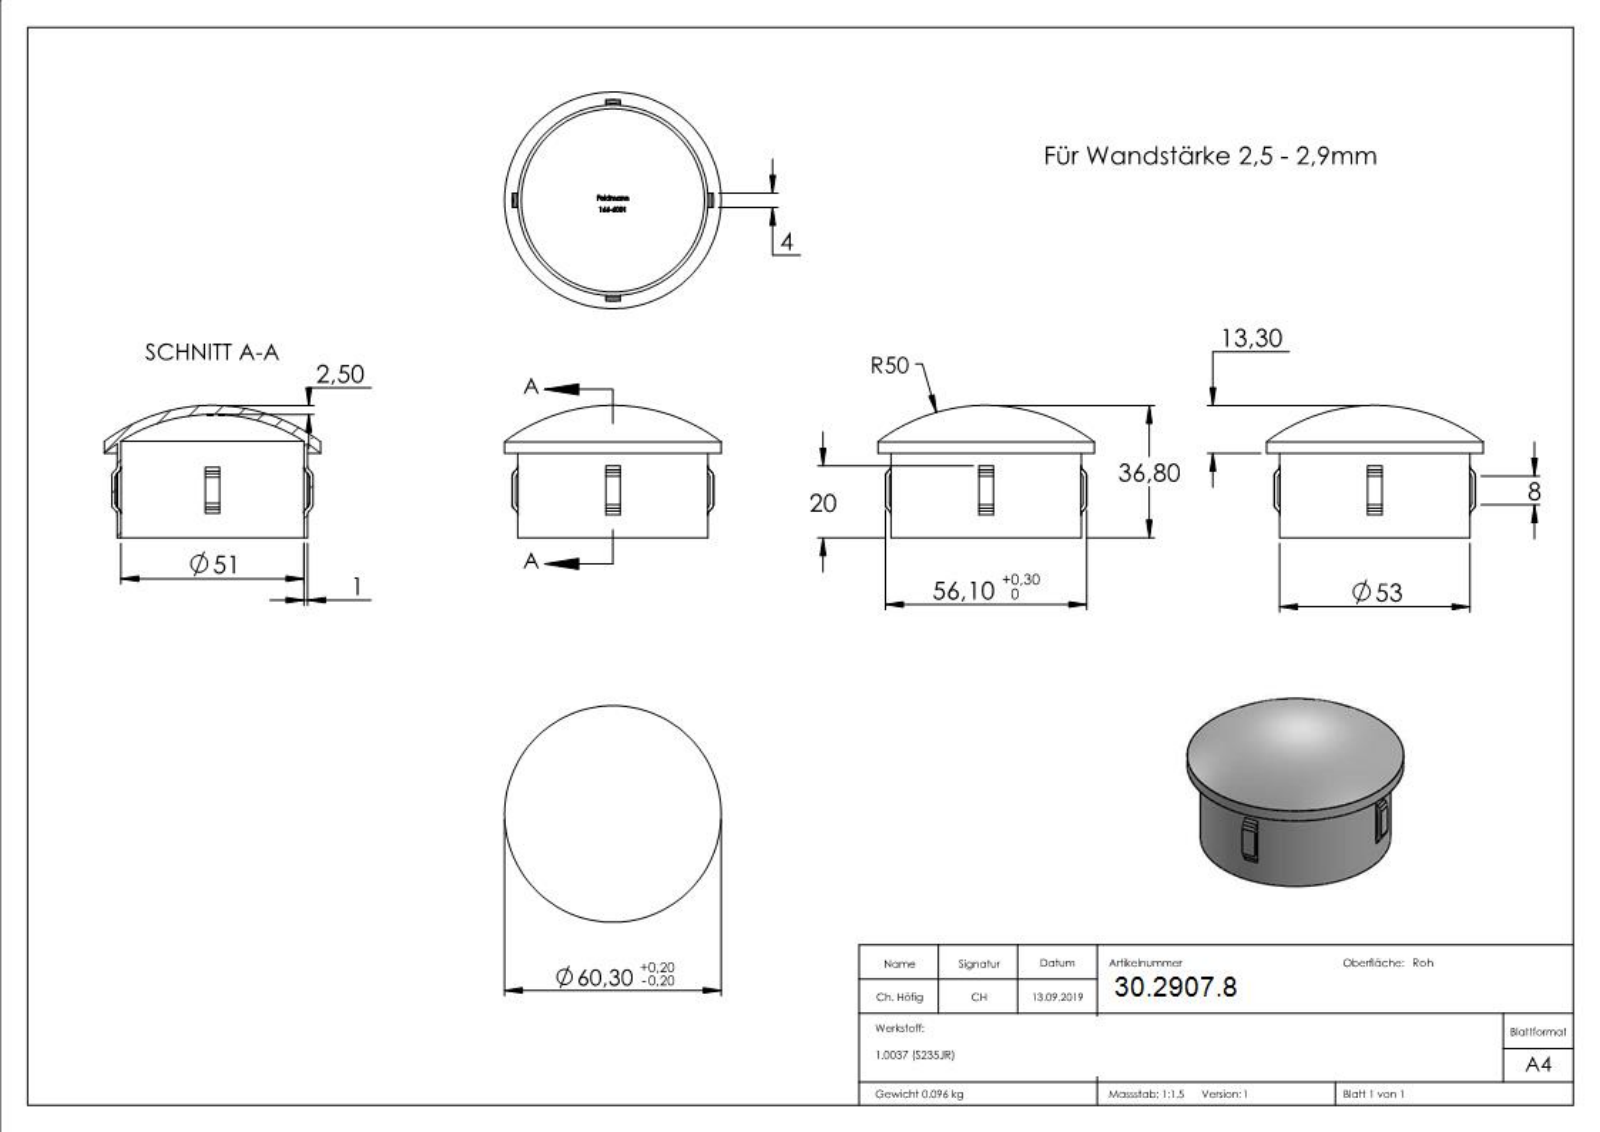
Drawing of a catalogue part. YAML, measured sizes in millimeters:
part_name: "166-6001"
step_written_by: "SolidWorks 2015 (CONFIG_CONTROL_DESIGN)"
units: millimeters
bodies: {solids: 1, faces: 304, planar: 96, cylindrical: 16, other: 192}
overall_size: [60.3, 60.3, 36.8]
volume: 12354
surface_area: 15864
round_holes:
  - {diameter: 51, count: 1}
round_bosses_or_shafts:
  - {diameter: 60.3, count: 1}
  - {diameter: 53, count: 1}
partial_cylinders:
  - {radius: 27.05, count: 1}
  - {radius: 28.05, count: 1}
face_to_face_distances: [4, 2.97, 2, 0.39, 1.26, 6.72, 3.27, 0.87, 7.59, 1.36]
